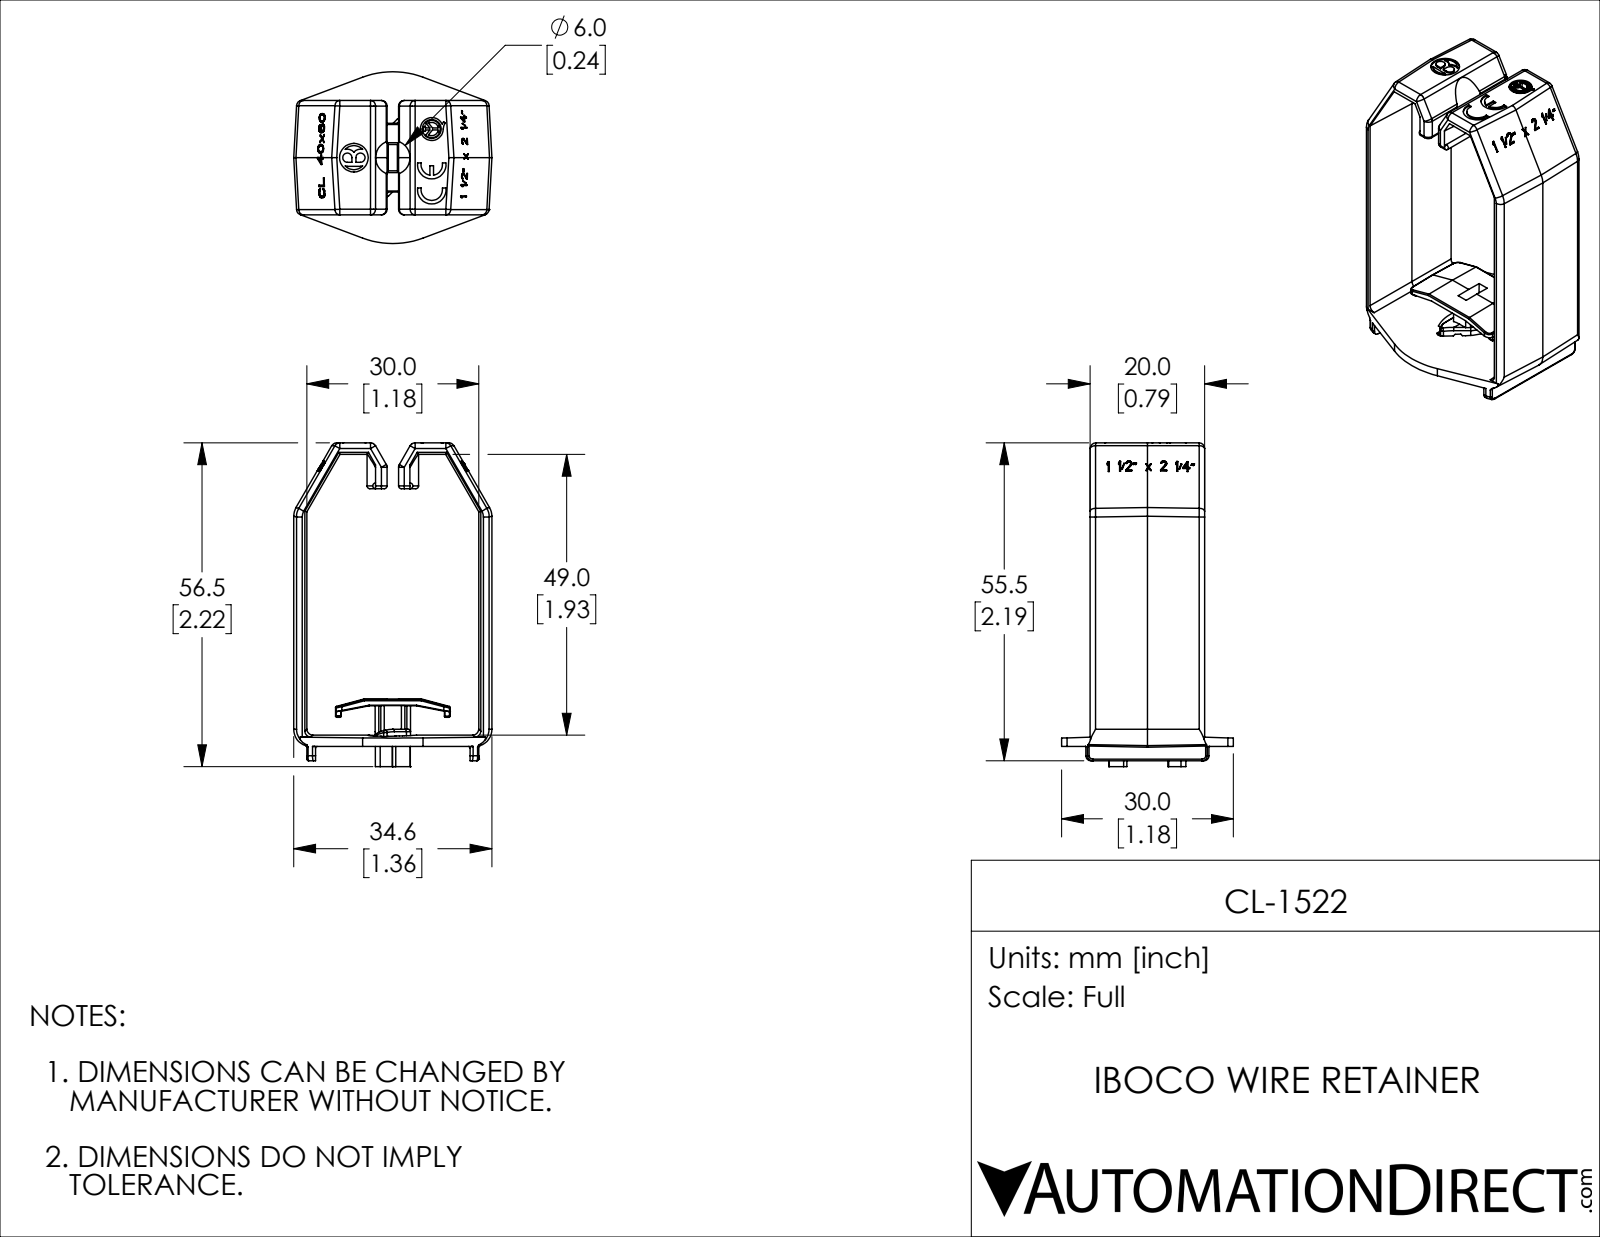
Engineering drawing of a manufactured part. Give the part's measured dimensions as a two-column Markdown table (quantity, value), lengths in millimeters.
| quantity | value |
| --- | --- |
| part name | CL-1522 |
| STEP written by | SolidWorks 2019 (CONFIG_CONTROL_DESIGN) |
| units | millimeters |
| bodies | 1 solid, 799 faces (561 planar, 180 cylindrical, 58 other) |
| overall size | 56.5 × 34.6 × 30 |
| volume | 6 620 mm³ |
| surface area | 8 484 mm² |
| round holes (diameter × count) | 4 × 1, 5 × 1 |
| round bosses / shafts (diameter × count) | 3.3 × 1 |
| partial cylindrical surfaces (radius × count) | 1 × 36, 0.2 × 22, 0.3 × 14, 0.5 × 12, 3 × 9, 0.4 × 6, 0.9 × 6, 2.5 × 4 |
| main face-to-face distances | 30, 34.6, 48.9, 53, 2, 4, 16, 12, 1.5, 28.5 |
| hole center spacings | 14.5 |
